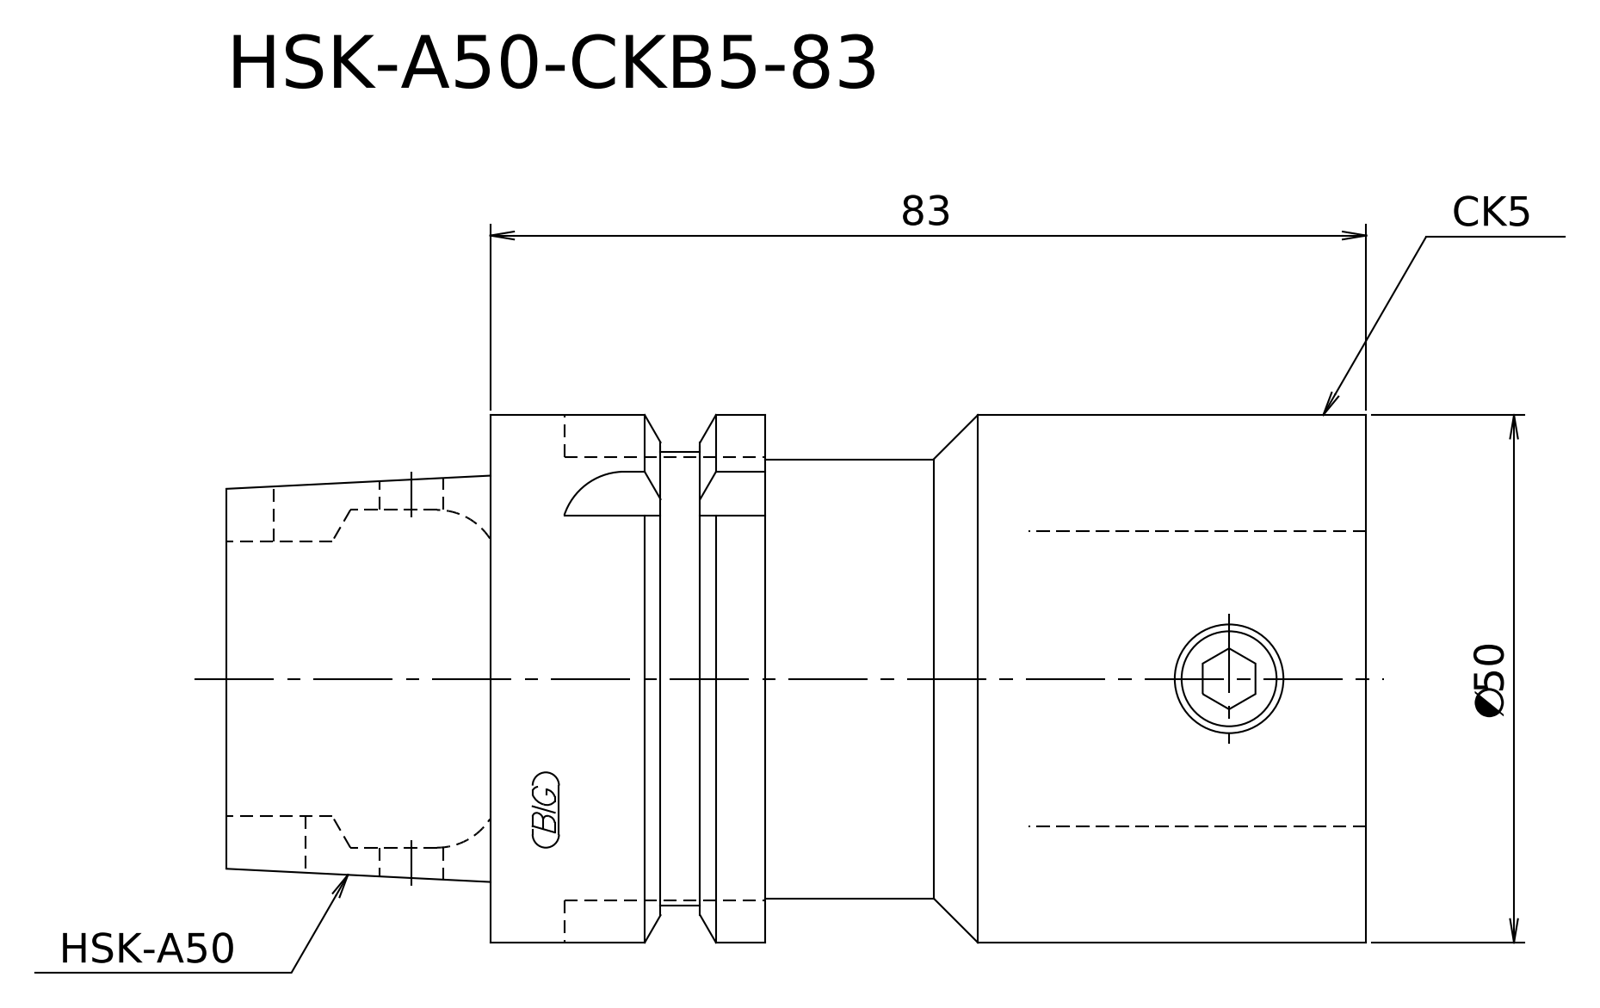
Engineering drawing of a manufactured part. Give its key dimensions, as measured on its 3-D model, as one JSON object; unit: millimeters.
{"step_written_by": "Kubotek KeyCreator V8.5.1 (14335) (CONFIG_CONTROL_DESIGN)", "units": "millimeters", "bodies": {"solids": 1, "faces": 16, "planar": 6, "cylindrical": 6, "other": 4}, "overall_size": [108, 50, 50], "volume_mm3": 176726, "surface_area_mm2": 20724, "round_bosses_or_shafts": [[50, 1], [43, 1], [41.6, 1], [38.3, 1]], "face_to_face_distances": [108, 83, 25, 57, 26, 51, 63.12, 6.12, 19.88, 44.88]}
